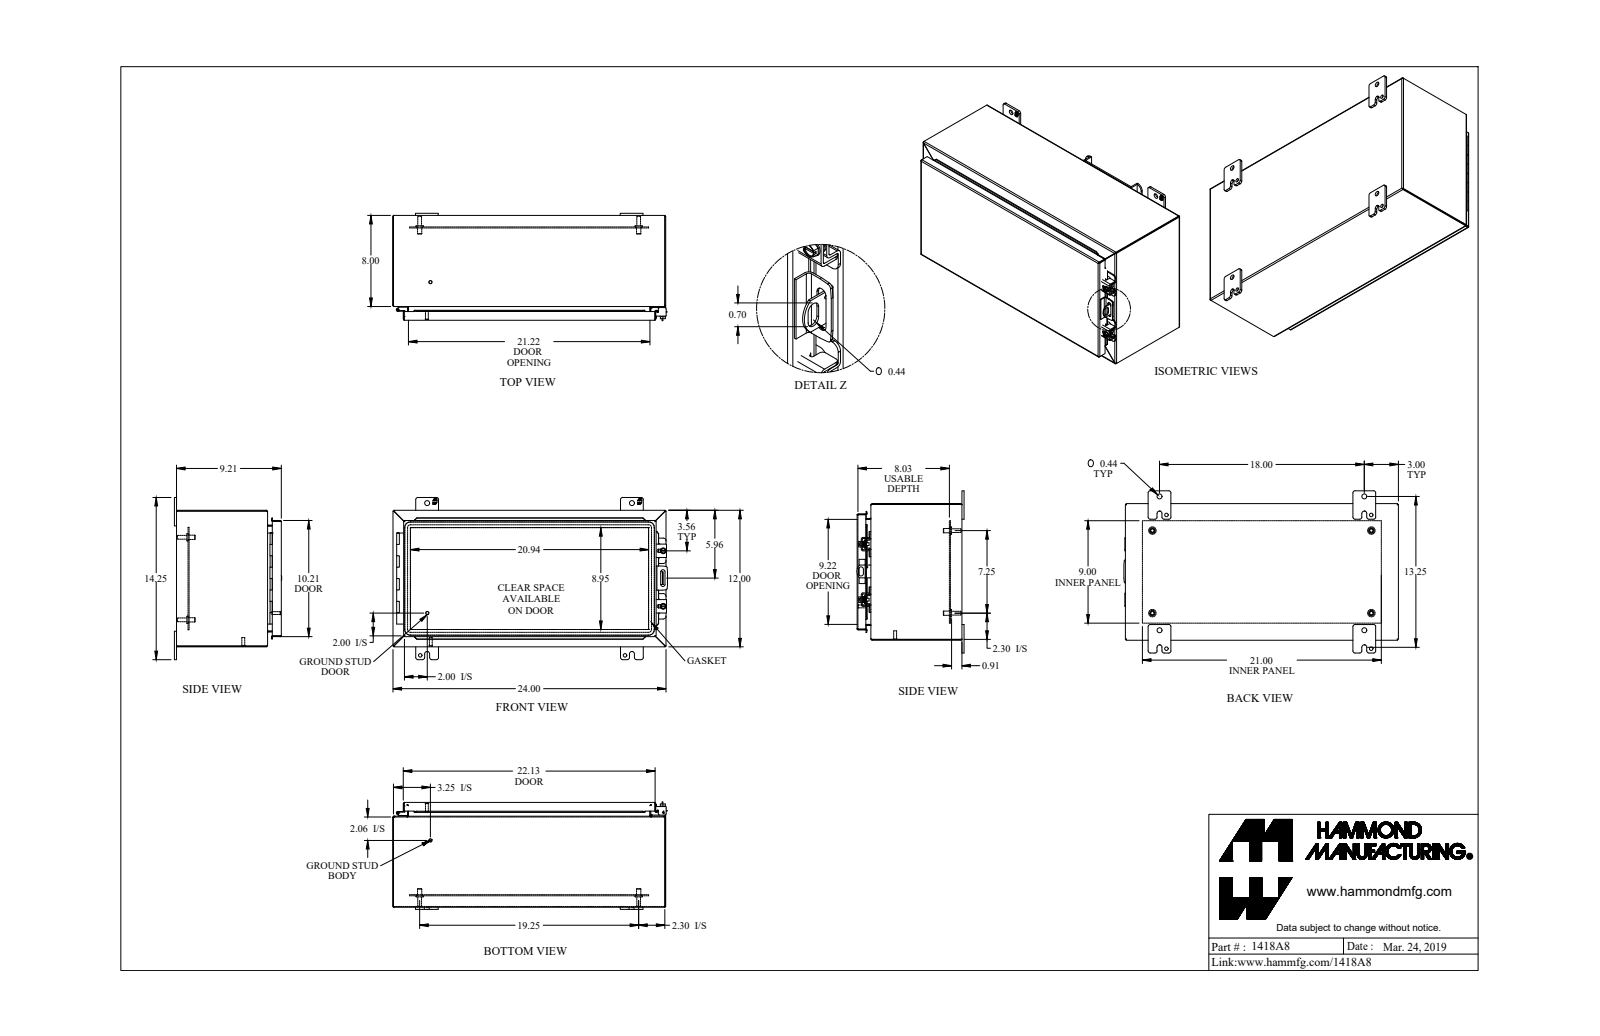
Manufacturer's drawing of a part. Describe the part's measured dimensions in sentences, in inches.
The part is named "1418A8". Its 3-D file was written by "SolidWorks 2019 (AUTOMOTIVE_DESIGN)". It is 37 solids with 929 faces: 636 planar, 241 cylindrical and 52 other. Overall it measures 24.125 by 14.25 by 9.437 inches. Its volume is 126.8 cubic inches and its surface area 3 297 square inches. Round holes: 4 of diameter 0.313, 4 of diameter 0.437, 4 of diameter 0.5, 2 of diameter 0.213, 2 of diameter 0.265, 2 of diameter 0.307, 2 of diameter 0.375, 2 of diameter 0.445, 1 of diameter 0.11, 1 of diameter 0.125. Round bosses or shafts: 4 of diameter 0.65, 4 of diameter 0.375, 4 of diameter 0.33, 2 of diameter 1, 2 of diameter 0.5, 2 of diameter 0.39, 2 of diameter 0.281, 2 of diameter 0.25. Partial cylindrical surfaces (rounded edges, fillets, slot ends): 26 of radius 0.188, 20 of radius 0.036, 20 of radius 0.108, 13 of radius 0.048, 13 of radius 0.143, 8 of radius 0.007, 8 of radius 0.045, 8 of radius 0.079. The main face-to-face distances are 0.072, 9.113, 11.928, 9.041, 9.185, 0.937, 1.009, 0.095, 8.081, 8.009. The hole center spacings are 18, 20.57, 21.496, 2.434, 3.065, 7.25, 18.865, 20.57.
